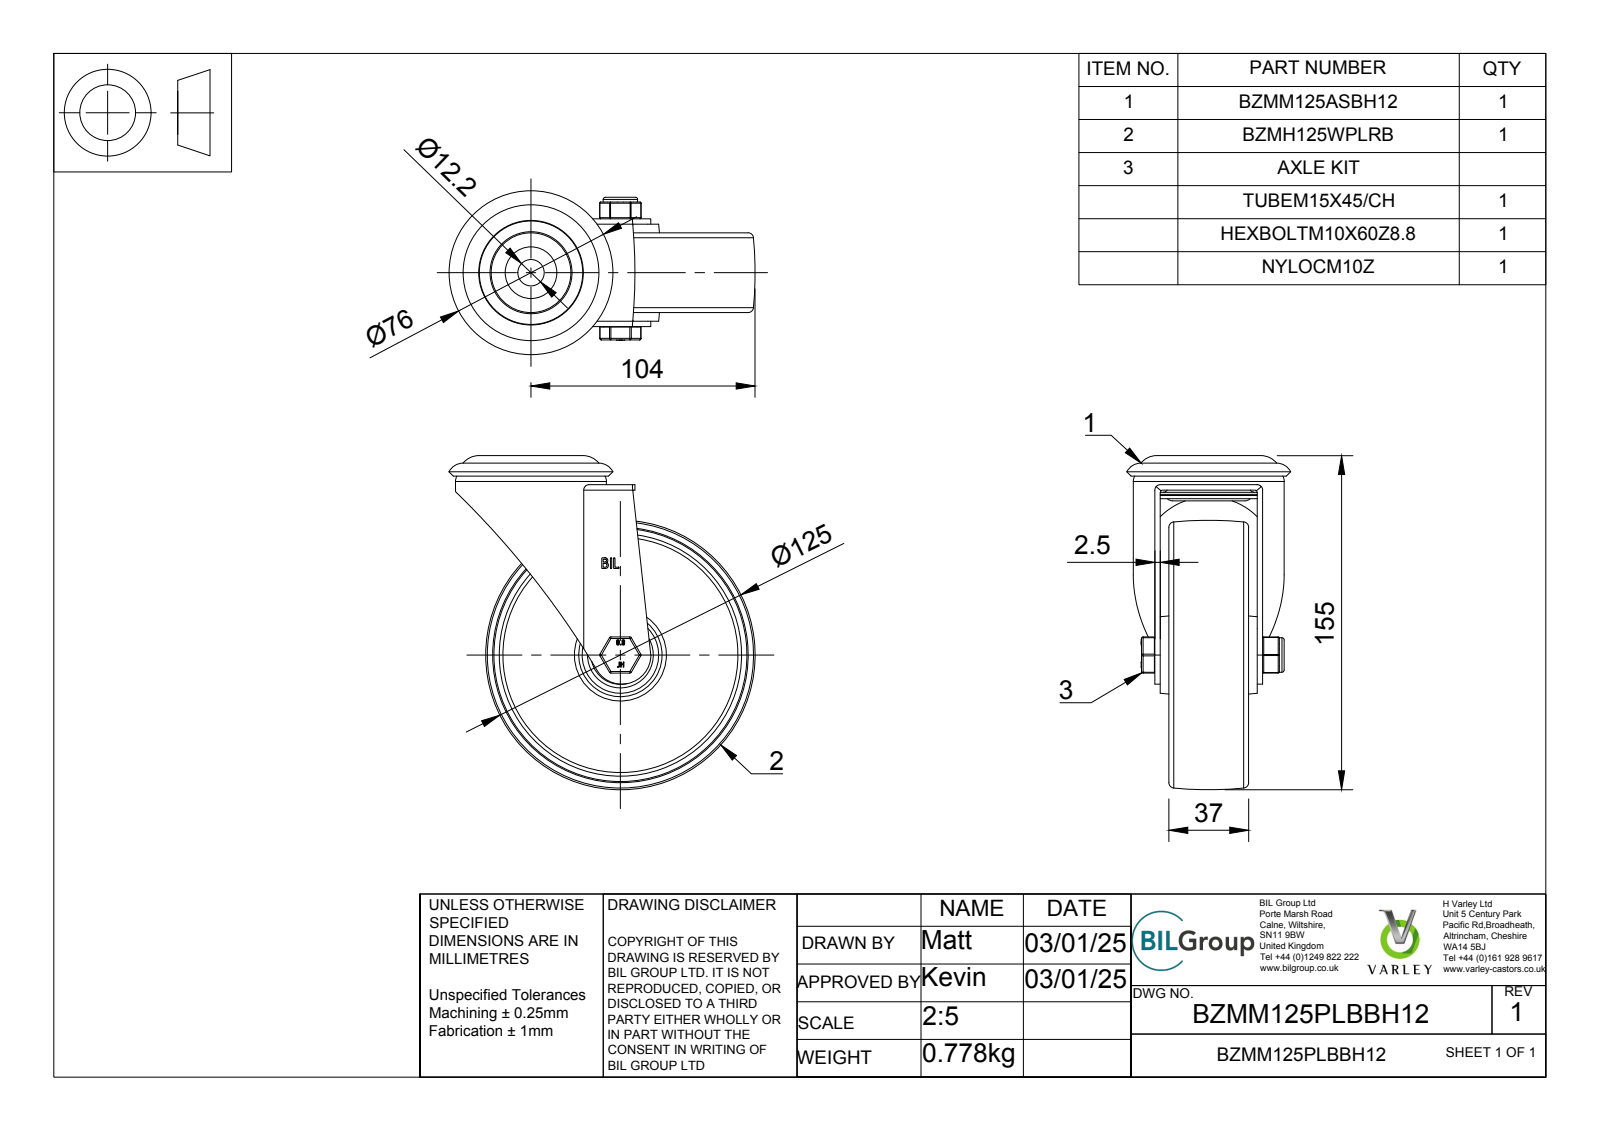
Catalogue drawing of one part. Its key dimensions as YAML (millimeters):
part_name: "BZMM125PLBBH12 v3; BZMM125ASBH12 v1; ZINC PLATED, PRESSED STEEL HEAD; ZINC PLATED, PRESSED STEEL FORKS (+7 more)"
step_written_by: "Autodesk Translation Framework v13.20.0.188 (AP242_MANAGED_MODEL_BASED_3D_ENGINEERING_MIM_LF)"
units: millimeters
bodies: {solids: 16, faces: 424, planar: 182, cylindrical: 132, other: 110}
overall_size: [155, 142, 76]
volume: 262459
surface_area: 119472
round_holes:
  - {diameter: 10, count: 1}
  - {diameter: 10.2, count: 1}
  - {diameter: 12, count: 1}
  - {diameter: 12.2, count: 1}
  - {diameter: 15.5, count: 1}
  - {diameter: 23, count: 1}
  - {diameter: 30.5, count: 1}
  - {diameter: 65, count: 1}
  - {diameter: 72, count: 1}
round_bosses_or_shafts:
  - {diameter: 4, count: 8}
  - {diameter: 70, count: 1}
  - {diameter: 49.5, count: 1}
  - {diameter: 38, count: 1}
  - {diameter: 24, count: 1}
  - {diameter: 21.31, count: 1}
  - {diameter: 16, count: 1}
  - {diameter: 14.95, count: 1}
partial_cylinders:
  - {radius: 0.5, count: 18}
  - {radius: 0.75, count: 12}
  - {radius: 1.25, count: 4}
  - {radius: 2.5, count: 2}
  - {radius: 9.5, count: 1}
  - {radius: 13.5, count: 1}
  - {radius: 253.62, count: 1}
  - {radius: 408.21, count: 1}
face_to_face_distances: [7, 2.5, 19, 26, 28.5, 21.5, 47.5, 45, 50, 6.5]
